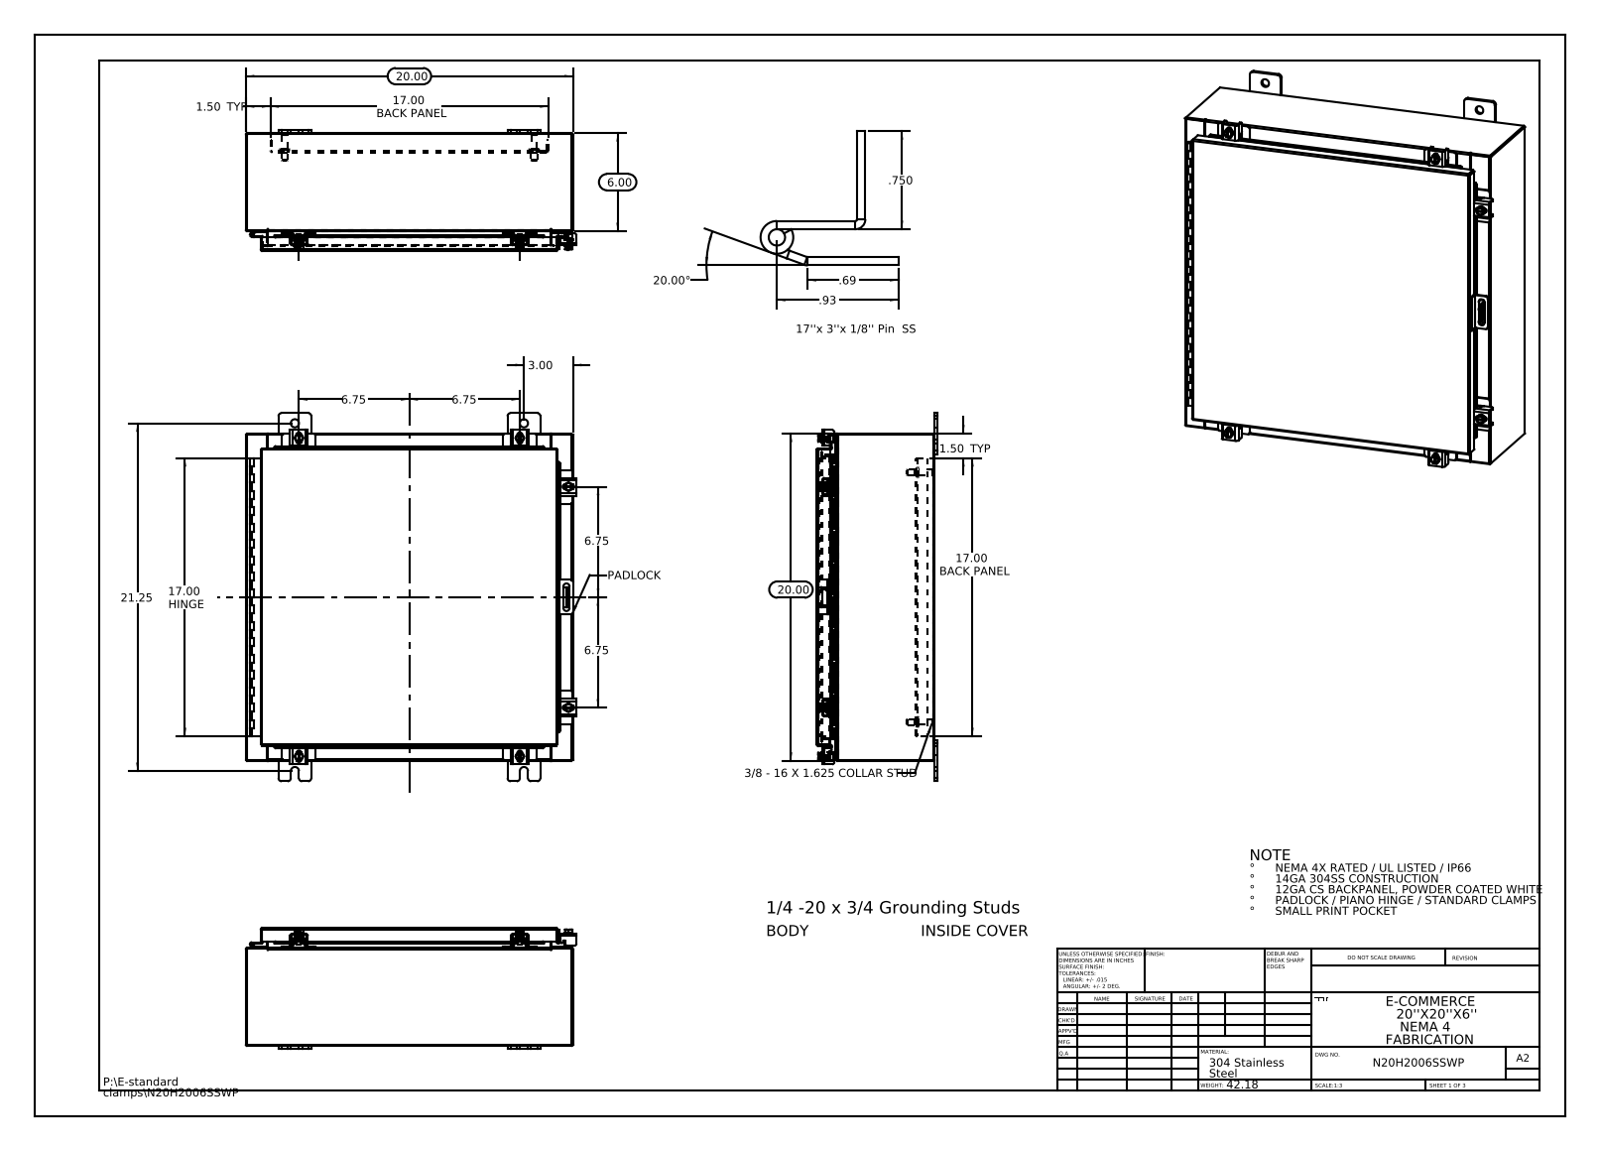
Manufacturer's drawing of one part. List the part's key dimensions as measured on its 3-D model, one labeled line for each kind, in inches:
Part name (STEP PRODUCT): N20H2006SSWP Mounting Feet; N20H2006SSWP Standard Clamps; N20H2006SSWP Backpanel; N20H2006SSWP 22104005_DEFAULT (+8 more)
STEP written by: SolidWorks 2013 (CONFIG_CONTROL_DESIGN)
Units: inches
Bodies: 47 solids, 1613 faces (860 planar, 657 cylindrical, 96 other)
Overall size (bounding box): 22.5 × 20.211 × 7.389
Volume: 148.9 in³ · Surface area: 3 740 in²
Round holes (diameter × count): ⌀0.5 ×8, ⌀0.213 ×6, ⌀0.26 ×6, ⌀0.125 ×2, ⌀0.125 ×1
Round bosses / shafts (diameter × count): ⌀0.25 ×7, ⌀0.5 ×6, ⌀0.399 ×6, ⌀0.625 ×4, ⌀0.375 ×4, ⌀0.33 ×4
Partial cylindrical surfaces — rounded edges, fillets, slot ends (radius × count): R0.06 ×30, R0.013 ×25, R0.19 ×24, R0.088 ×21, R0.12 ×12, R0.141 ×12, R0.125 ×10, R0.05 ×9
Main face-to-face distances: 0.075, 7.126, 19.925, 7.201, 7.051, 0.104, 1, 1.075, 6.051, 6.126
Hole centre spacings: 17.373, 14.528, 16.742, 22.532, 13.5, 0.431, 0.934, 1.858
